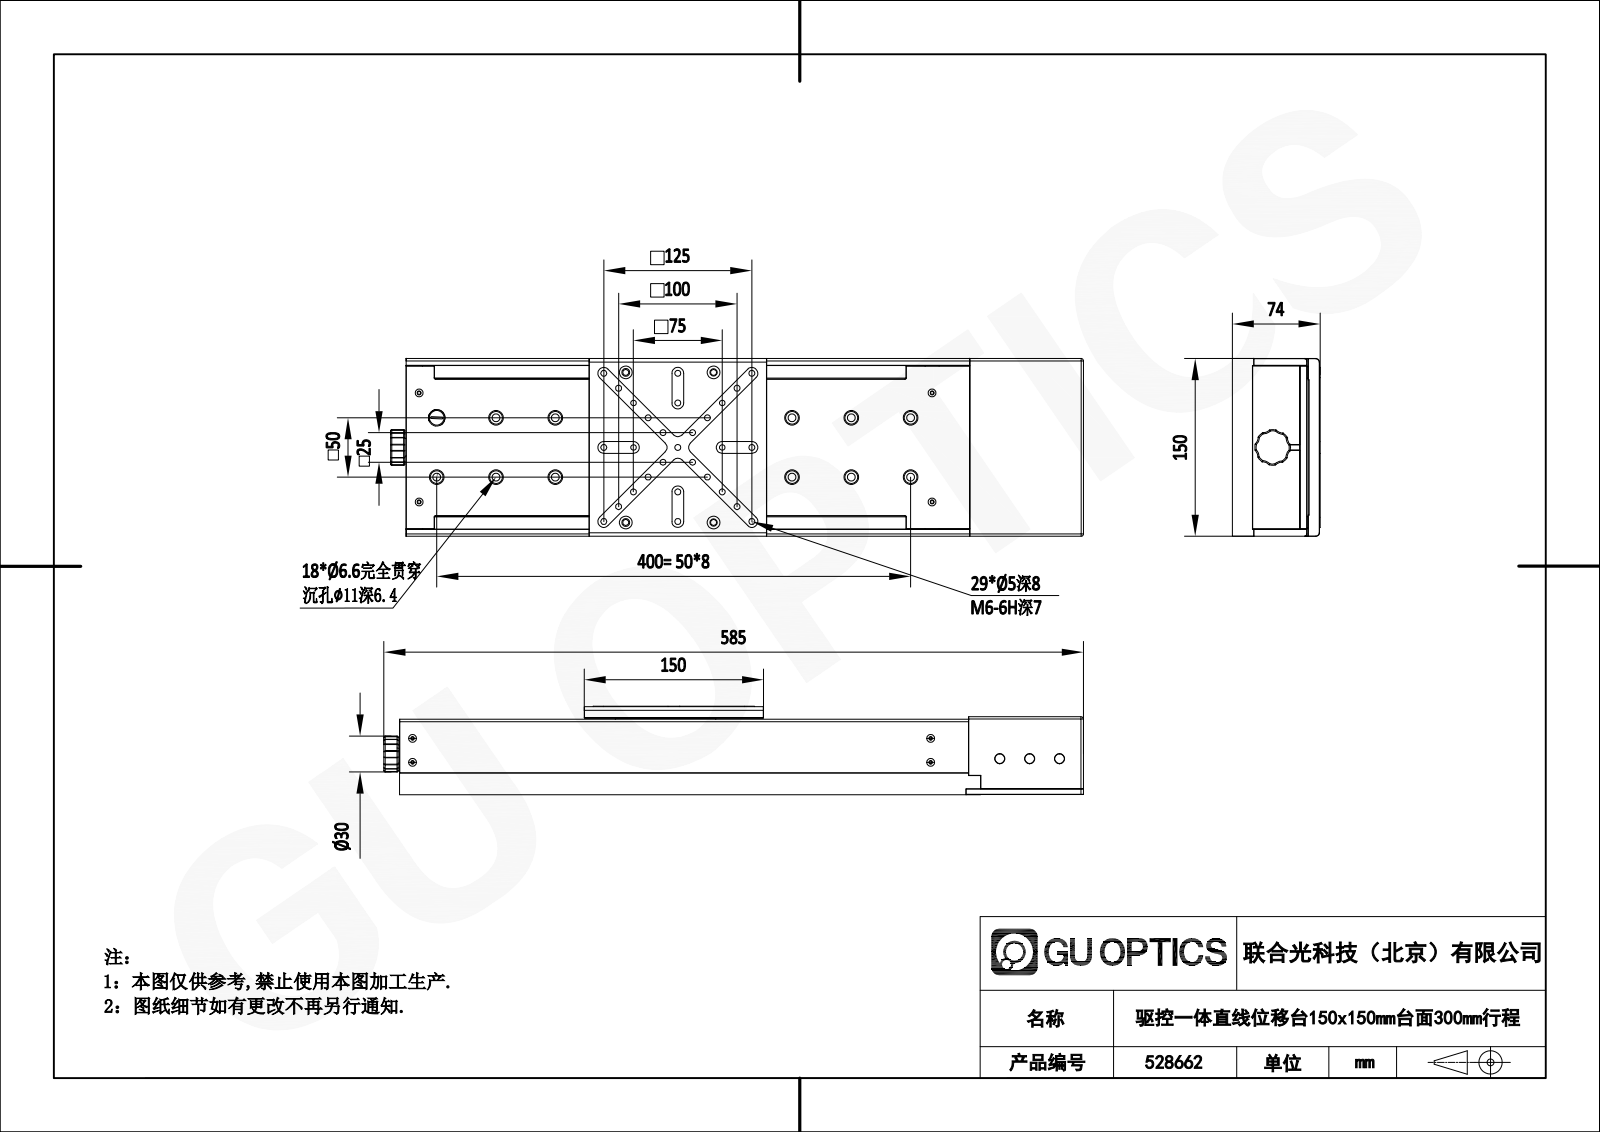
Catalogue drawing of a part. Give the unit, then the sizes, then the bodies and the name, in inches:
Units: inches
Overall size (bounding box): 23.031 × 5.906 × 2.913
Round holes (diameter × count): ⌀0.197 ×40, ⌀0.134 ×27, ⌀0.26 ×24, ⌀0.433 ×24, ⌀0.256 ×19, ⌀0.492 ×18, ⌀0.097 ×16, ⌀0.138 ×16, ⌀0.098 ×15, ⌀0.236 ×12, ⌀0.13 ×9, ⌀0.177 ×6
Round bosses / shafts (diameter × count): ⌀1.504 ×1, ⌀0.945 ×1, ⌀0.748 ×1, ⌀0.63 ×1, ⌀0.551 ×1, ⌀0.416 ×1, ⌀0.118 ×1
Partial cylindrical surfaces — rounded edges, fillets, slot ends (radius × count): R0.039 ×20, R0.197 ×16, R0.079 ×13, R0.295 ×8, R0.157 ×5, R0.059 ×4, R0.012 ×2, R0.03 ×2
Main face-to-face distances: 0.236, 1.535, 2.244, 0.709, 2.48, 0.039, 1.772, 5.669, 5.906, 0.669
Hole centre spacings: 2.029, 2.461, 3.48, 0.984, 1.476, 2.65, 2.87, 4.643
Volume: 210.7 in³ · Surface area: 1 199 in²
Bodies: 45 solids, 2663 faces (1414 planar, 800 cylindrical, 449 other)
Part name (STEP PRODUCT): 528662
STEP written by: SolidWorks 2020 (CONFIG_CONTROL_DESIGN)
